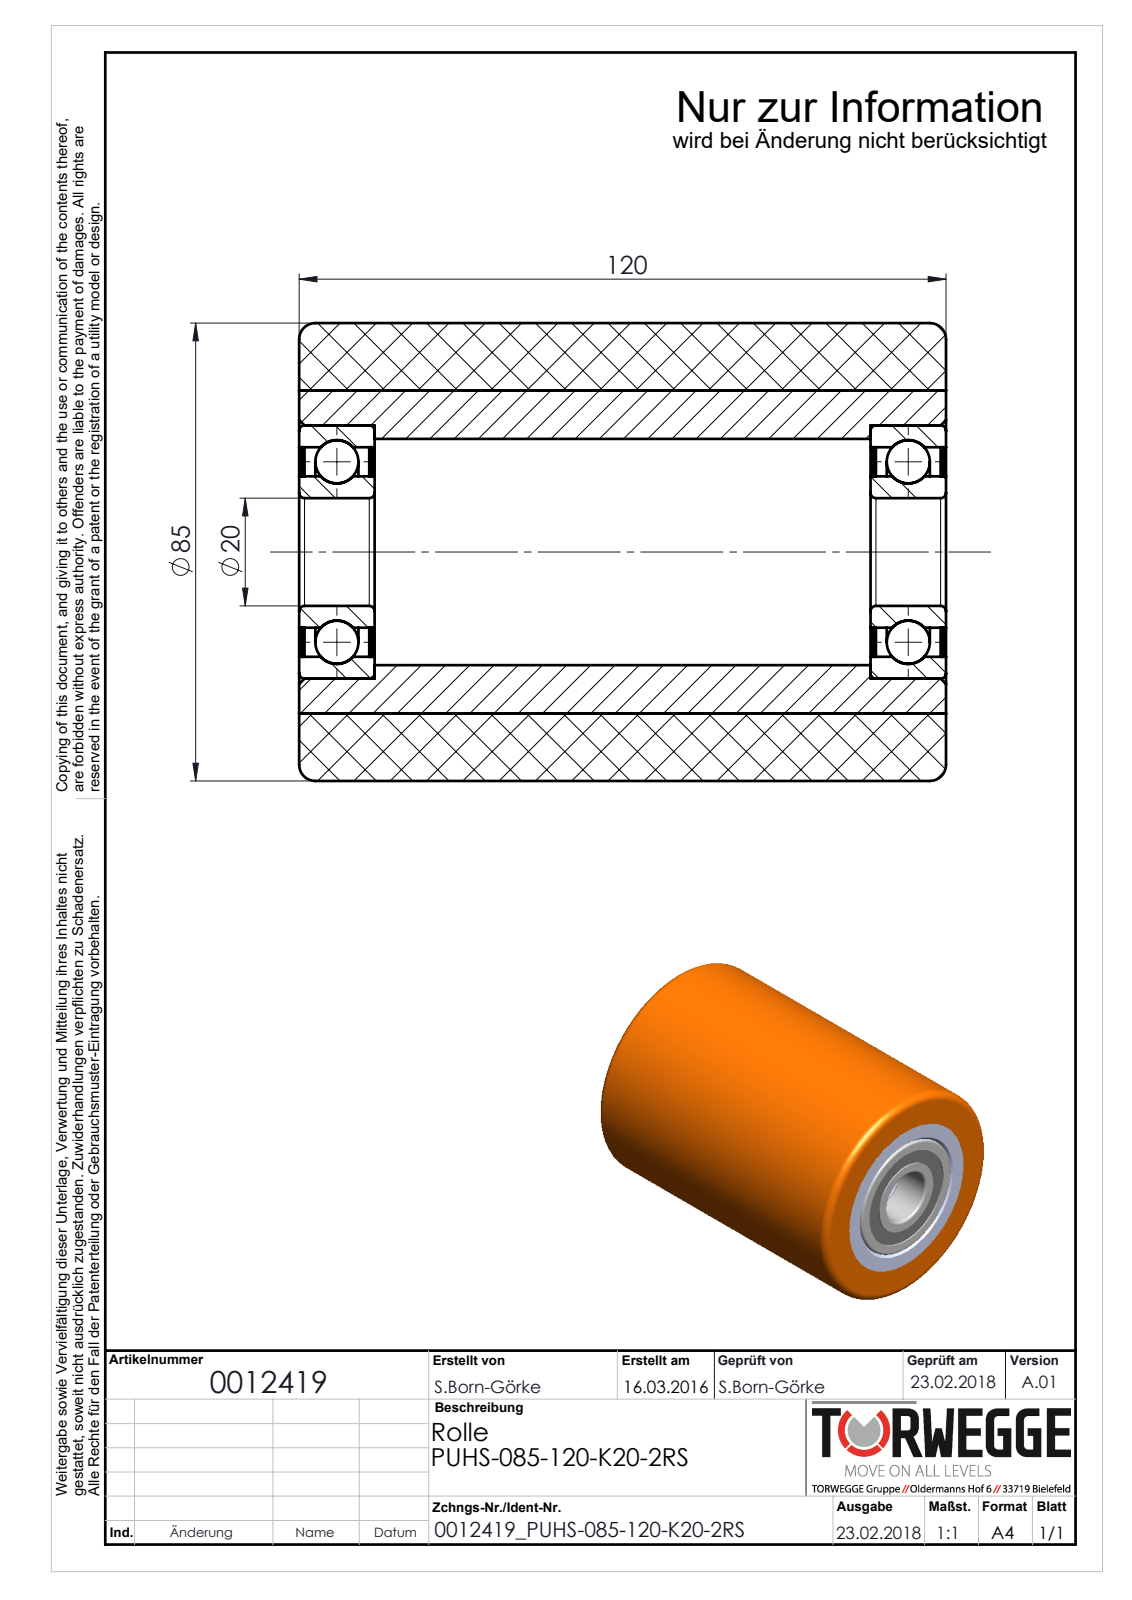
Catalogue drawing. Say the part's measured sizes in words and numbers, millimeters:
The part is named "K0012419_PUHS-085-120-K20-2RS". Its 3-D file was written by "SolidWorks 2016 (AUTOMOTIVE_DESIGN)". It is 12 solids with 118 faces: 22 planar, 52 cylindrical and 44 other. Overall it measures 120 by 85 by 85 millimeters. Its volume is 536 620 cubic millimeters and its surface area 126 705 square millimeters. Round holes: 1 of diameter 20, 1 of diameter 28.1, 1 of diameter 38.9, 1 of diameter 42, 1 of diameter 47, 1 of diameter 60. Round bosses or shafts: 1 of diameter 85. The main face-to-face distances are 0.5, 106, 120, 13, 1, 13.5, 106.5, 12.5, 105.5, 14.
